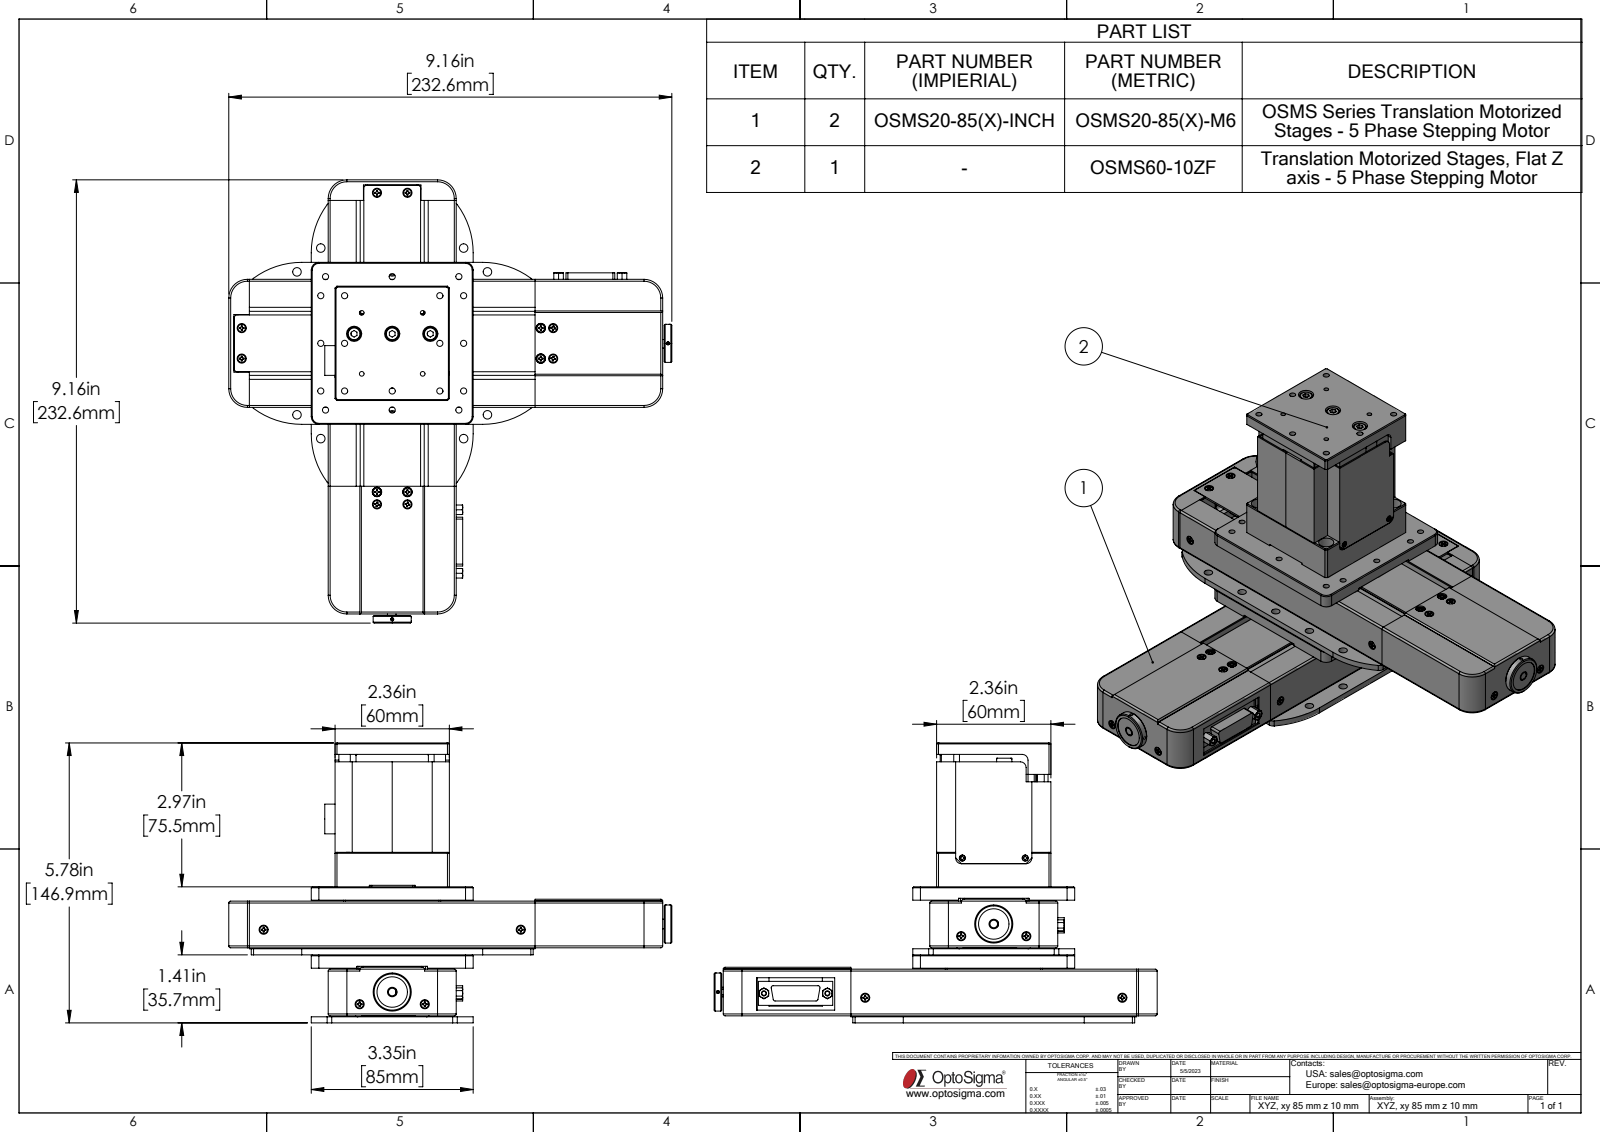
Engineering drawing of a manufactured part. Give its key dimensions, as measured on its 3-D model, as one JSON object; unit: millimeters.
{"part_name": "OSMS2085-M02-13001-S08^OSMS20-85(X)(2)_OSMS20-85 (X); OSZF6010-M02-13001-S25^OSMS60-10ZF(2)_OSMS60-10ZF; XYZ, xy 85 mm z 10 mm; OSMS60-10ZF(2)^OSMS60-10ZF (+5 more)", "step_written_by": "SolidWorks 2022 (AUTOMOTIVE_DESIGN)", "units": "millimeters", "bodies": {"solids": 36, "faces": 8142, "planar": 4001, "cylindrical": 1743, "other": 2398}, "overall_size": [232.6, 232.6, 146.9], "volume_mm3": 479330, "surface_area_mm2": 419880, "round_holes": [[3, 20], [2.6, 18], [2, 17], [1.57, 9], [3.1, 8], [3.2, 8], [4, 5], [1.6, 4], [4.2, 4], [6, 3], [16, 3], [1.5, 2]], "round_bosses_or_shafts": [[3, 54], [5.5, 45], [4.5, 36], [4, 28], [2, 17], [2.6, 16], [6, 8], [5.9, 8]], "partial_cylinders_radius": [[0.5, 159], [3, 63], [0.7, 52], [1, 32], [0.2, 16], [2, 16], [9, 9], [0.26, 8]], "face_to_face_distances": [35.7, 0.8, 23.7, 28.2, 3.7, 7.5, 0.5, 25, 24.2, 1.3], "hole_center_spacings": [12, 33.6, 35.68, 9, 24, 7.43, 8.77, 10.87]}
